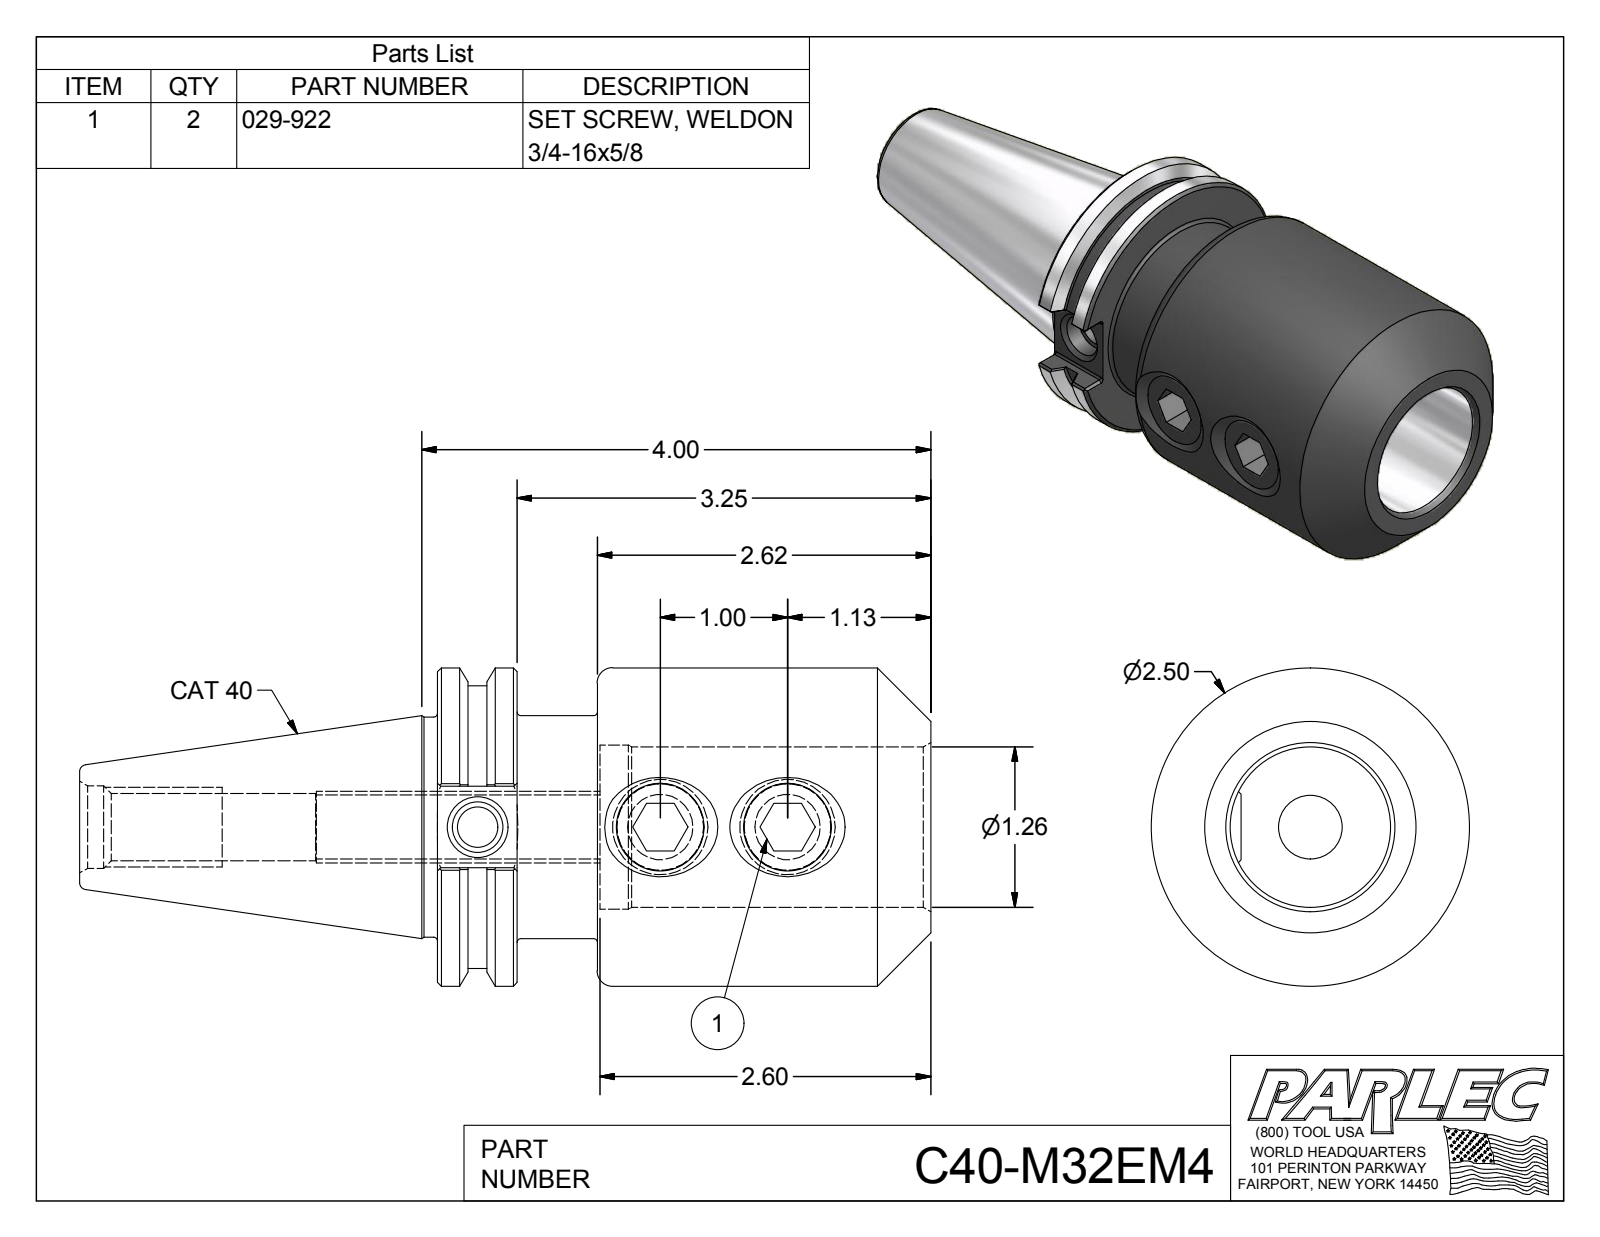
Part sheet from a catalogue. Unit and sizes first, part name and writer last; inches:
Units: inches
Overall size (bounding box): 6.687 × 2.5 × 2.5
Round holes (diameter × count): ⌀0.682 ×2, ⌀0.315 ×1, ⌀0.399 ×1, ⌀0.502 ×1, ⌀0.527 ×1, ⌀0.648 ×1, ⌀1.26 ×1, ⌀1.29 ×1
Round bosses / shafts (diameter × count): ⌀0.75 ×2, ⌀2.5 ×1, ⌀2.219 ×1, ⌀1.75 ×1, ⌀1.73 ×1
Partial cylindrical surfaces — rounded edges, fillets, slot ends (radius × count): R0.02 ×12
Main face-to-face distances: 0.625, 1.255, 0.63, 1.275, 0.65, 0.02, 3.875, 3.25, 2.62, 2.6
Hole centre spacings: 1, 1.435, 2.435
Volume: 16.46 in³ · Surface area: 75.11 in²
Bodies: 3 solids, 120 faces (51 planar, 32 cylindrical, 37 other)
Part name (STEP PRODUCT): C40-M32EM4; C40-M32EM4-1; 029-922
STEP written by: Autodesk Inventor 2012 (AUTOMOTIVE_DESIGN)
